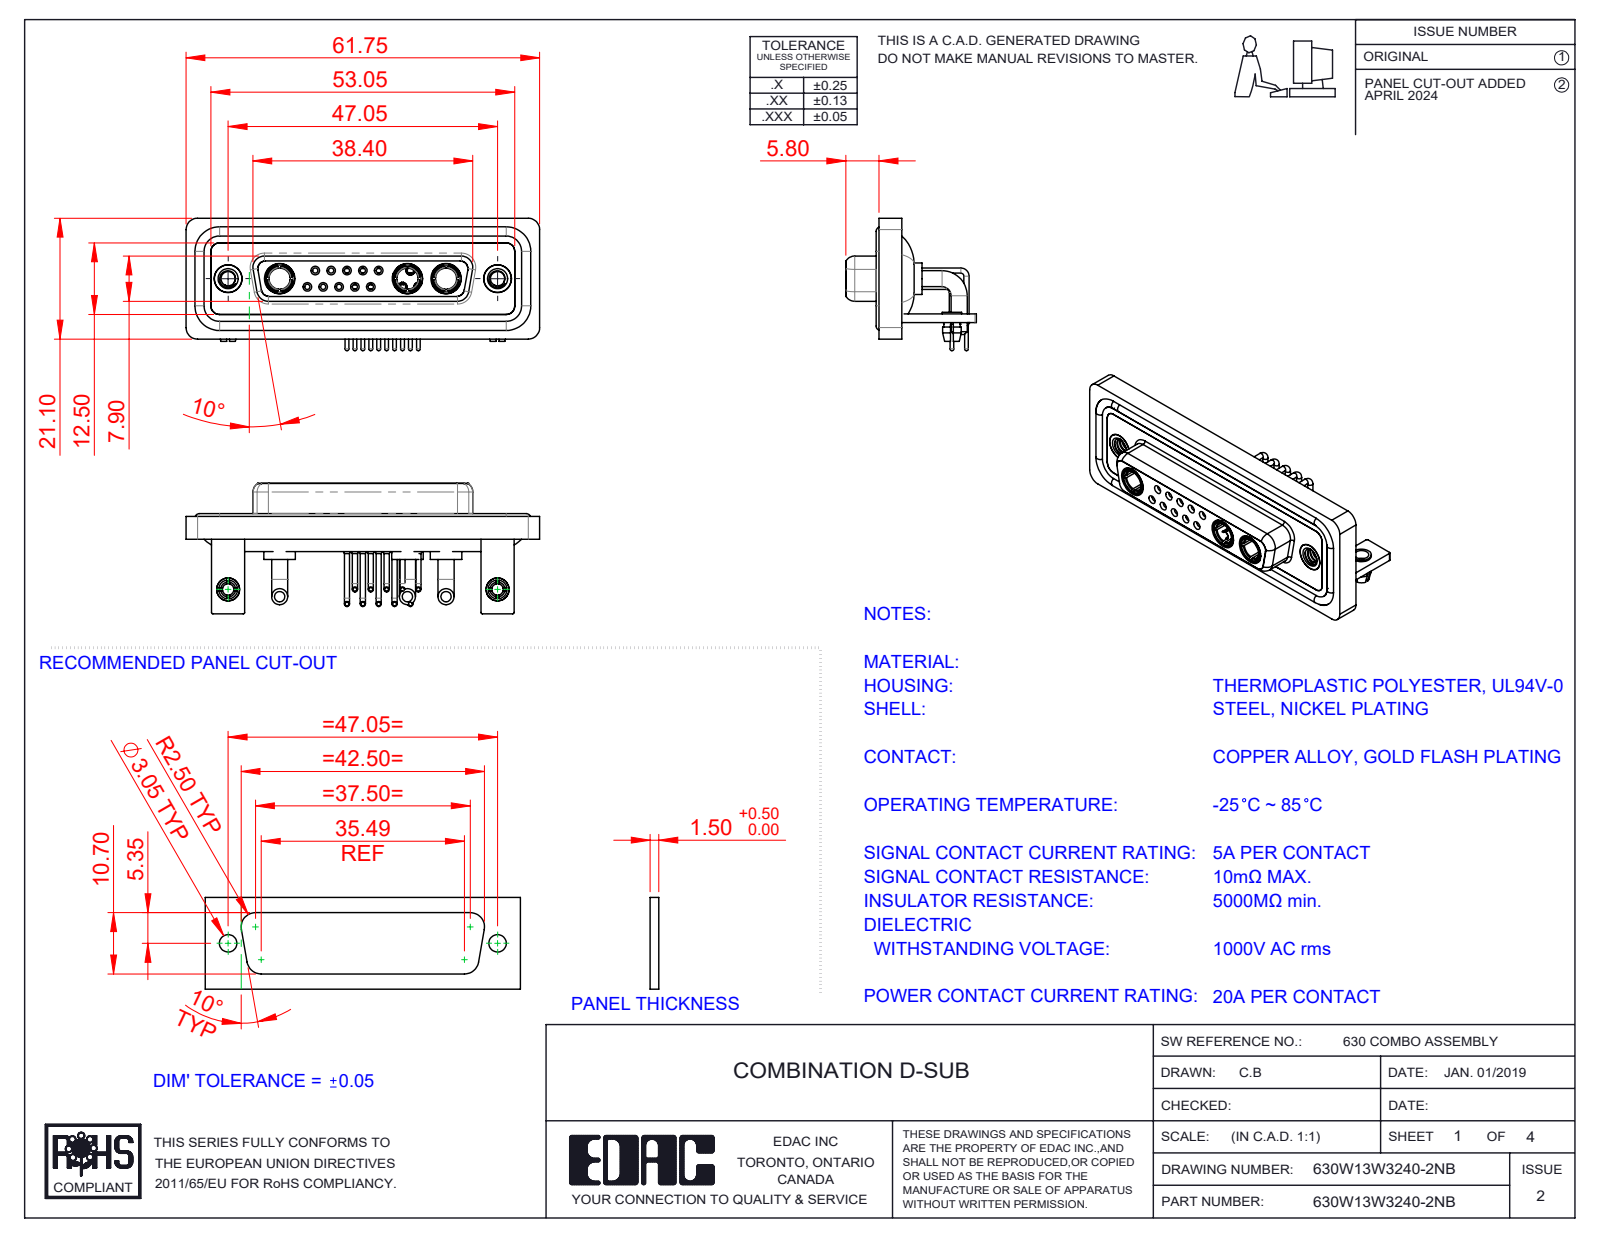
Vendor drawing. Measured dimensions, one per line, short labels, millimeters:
name: Power Socket_20A RA; 630Combo Shell Rear_25 Contacts; 630Combo Threaded Rivet_A; 630Combo Shell Front_25 Contacts (+7 more)
written by: SolidWorks 2023 (CONFIG_CONTROL_DESIGN)
unit: mm
bodies: 27 solids, 1284 faces (410 planar, 547 cylindrical, 327 other)
size: 61.75 × 23.12 × 22.8
volume: 8 866 mm³; area: 15 245 mm²
holes: 12× ⌀2, 10× ⌀0.9, 10× ⌀1.1, 10× ⌀1.5, 5× ⌀1.6, 5× ⌀1.7, 5× ⌀4.85, 4× ⌀2.5, 3× ⌀3.7, 3× ⌀5.3, 2× ⌀3.2, 2× ⌀4
bosses: 15× ⌀0.9, 12× ⌀1.6, 10× ⌀0.65, 6× ⌀2.8, 5× ⌀2, 5× ⌀1.5, 3× ⌀5.5, 3× ⌀5.2
rounds: 19× R2, 18× R1.5, 16× R0.25, 8× R1.35, 8× R1.6, 5× R0.5, 4× R0.6, 4× R0.65
face distances: 0.4, 1.8, 2.9, 1.5, 3.7, 4.1, 1.1, 1.4, 1.6, 3.1
hole spacings: 3.16, 2.77, 5.54, 5.04, 8.31, 5.03, 7.49, 11.08
